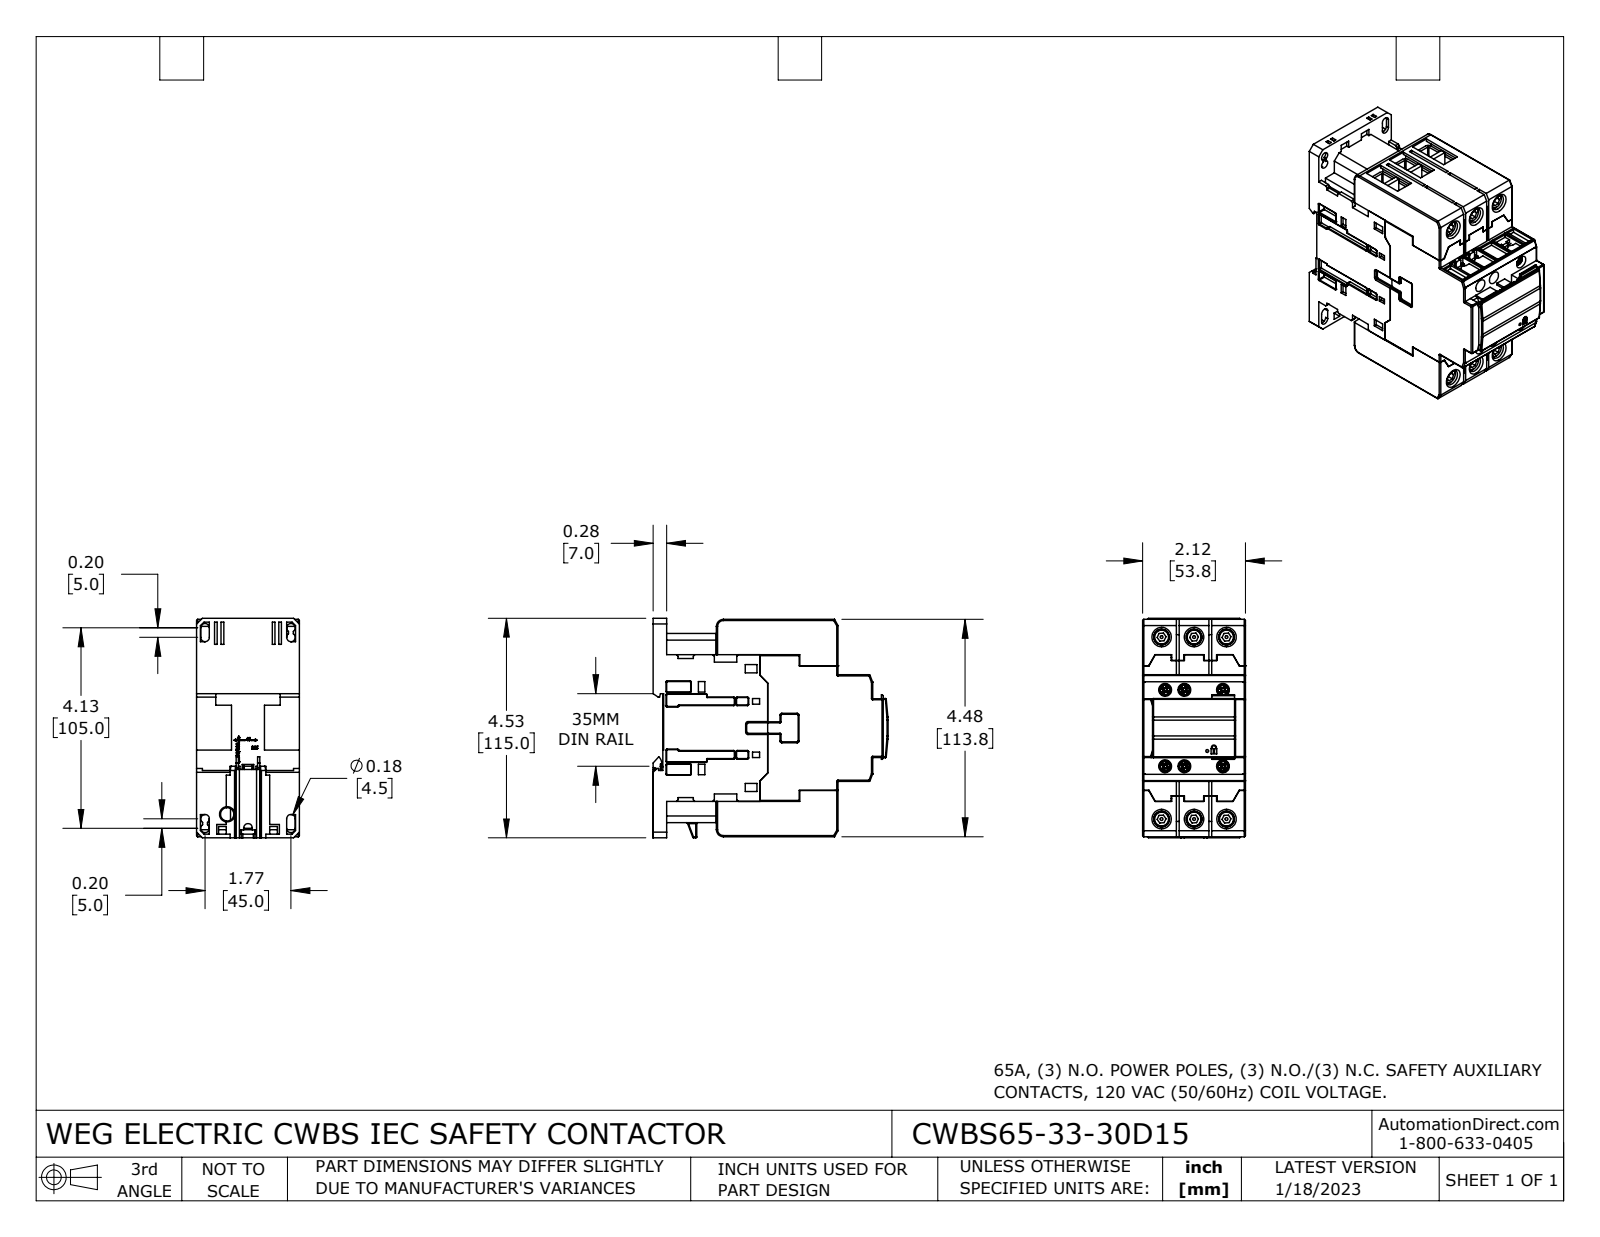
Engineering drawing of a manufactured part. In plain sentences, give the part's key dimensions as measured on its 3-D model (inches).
The part is named "CWBS65-33-30D15". Its 3-D file was written by "SolidWorks 2021 (CONFIG_CONTROL_DESIGN)". It is 37 solids with 2637 faces: 1669 planar, 550 cylindrical and 418 other. Overall it measures 4.846 by 4.528 by 2.118 inches. Its volume is 33.67 cubic inches and its surface area 209.3 square inches. Round holes: 6 of diameter 0.124, 6 of diameter 0.197, 6 of diameter 0.264, 6 of diameter 0.323, 4 of diameter 0.177, 2 of diameter 0.125, 2 of diameter 0.276, 1 of diameter 0.059. Round bosses or shafts: 6 of diameter 0.343, 6 of diameter 0.236, 6 of diameter 0.135. Partial cylindrical surfaces (rounded edges, fillets, slot ends): 89 of radius 0.02, 69 of radius 0.012, 48 of radius 0.004, 42 of radius 0.024, 18 of radius 0.079, 5 of radius 0.089, 3 of radius 0.039, 3 of radius 0.059. The main face-to-face distances are 0.059, 2.118, 0.669, 0.728, 3.024, 3.752, 0.108, 0.217, 3.811, 0.098. The hole center spacings are 0.669, 1.091, 1.241, 1.669, 2.665, 2.73, 2.949, 3.811.
